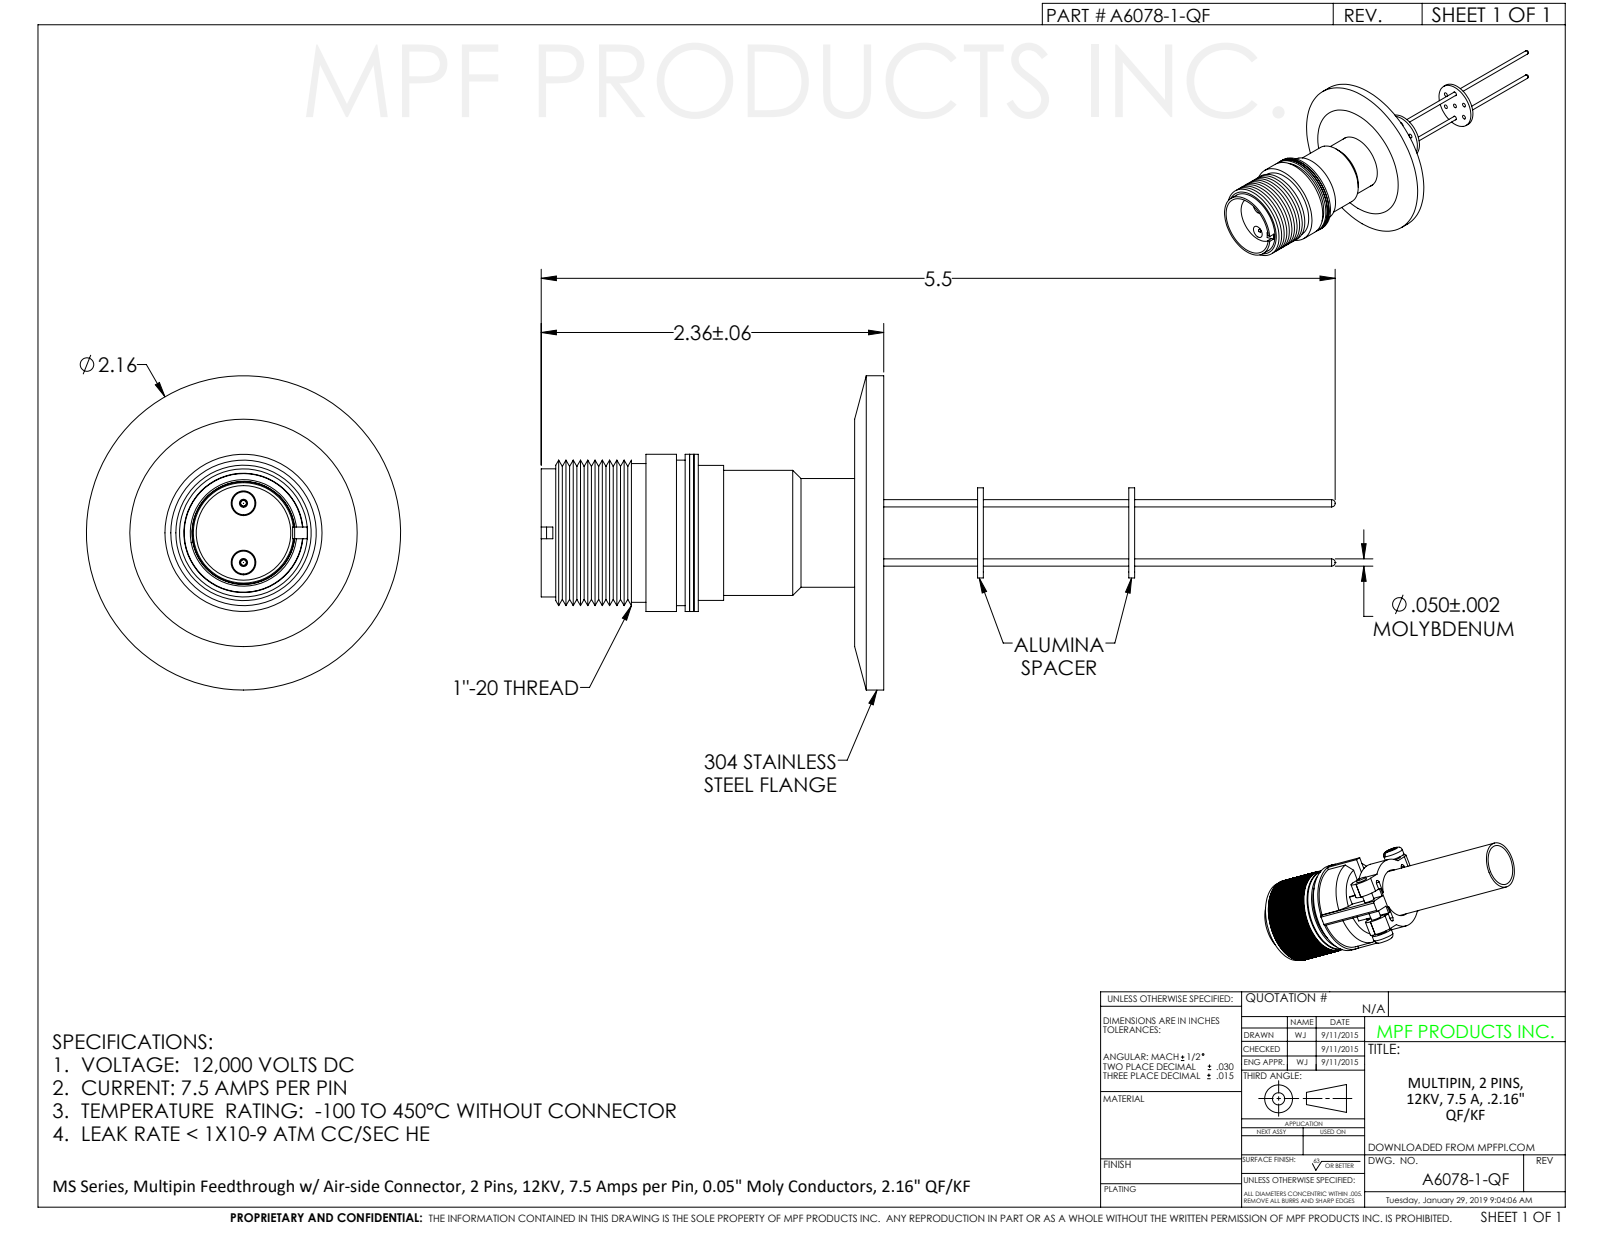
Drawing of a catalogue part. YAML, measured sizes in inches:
part_name: "A6078-1-QF"
step_written_by: "SolidWorks 2011 (CONFIG_CONTROL_DESIGN)"
units: inches
bodies: {solids: 1, faces: 227, planar: 38, cylindrical: 99, other: 90}
overall_size: [5.464, 2.161, 2.161]
volume: 1.332
surface_area: 31.01
round_holes:
  - {diameter: 0.036, count: 5}
  - {diameter: 0.054, count: 2}
  - {diameter: 0.056, count: 2}
  - {diameter: 0.152, count: 2}
  - {diameter: 0.687, count: 1}
  - {diameter: 0.791, count: 1}
  - {diameter: 0.8, count: 1}
  - {diameter: 0.82, count: 1}
  - {diameter: 1.63, count: 1}
round_bosses_or_shafts:
  - {diameter: 0.117, count: 2}
  - {diameter: 0.05, count: 2}
  - {diameter: 0.04, count: 2}
  - {diameter: 2.161, count: 1}
  - {diameter: 1.08, count: 1}
  - {diameter: 1, count: 1}
  - {diameter: 0.954, count: 1}
  - {diameter: 0.928, count: 1}
face_to_face_distances: [0.105, 0.095, 0.2, 1.5, 1.948, 0.448, 0.543, 0.648, 1.327, 0.879]
hole_center_spacings: [0.204, 0.352, 0.407, 0.203, 0.353]
